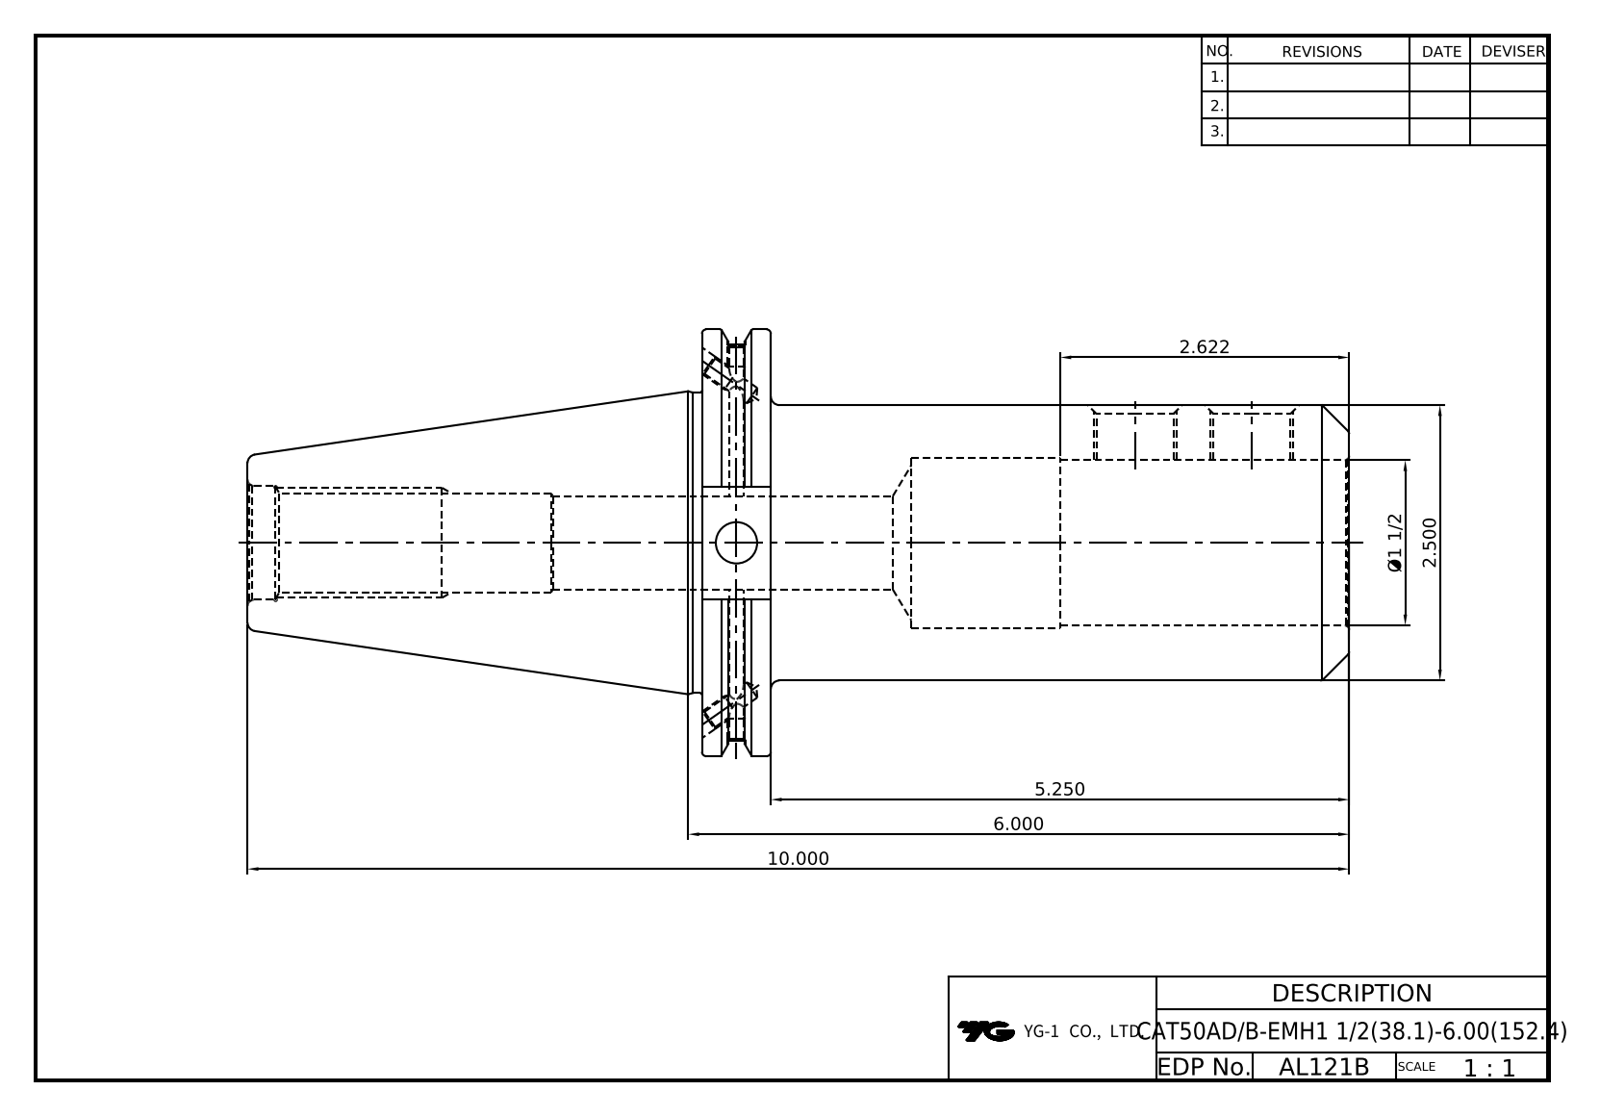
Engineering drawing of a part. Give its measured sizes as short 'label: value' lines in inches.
name: LO-CAT50ADB-EMH38.1-152.4
written by: Autodesk Inventor 2025 (AUTOMOTIVE_DESIGN)
unit: in
bodies: 1 solid, 87 faces (37 planar, 27 cylindrical, 23 other)
size: 10 × 3.875 × 3.728
volume: 36.65 in³; area: 132.1 in²
holes: 2× ⌀0.128, 2× ⌀0.163, 2× ⌀0.165, 2× ⌀0.197, 2× ⌀0.682, 1× ⌀0.375, 1× ⌀0.865, 1× ⌀1.031, 1× ⌀1.5, 1× ⌀1.547
bosses: 1× ⌀3.875, 1× ⌀3.594, 1× ⌀2.726, 1× ⌀2.5
face distances: 0.625, 1.899, 1.274, 5.875, 5.25, 3.976, 4.125, 4.75, 6.024, 10
hole spacings: 1.063
